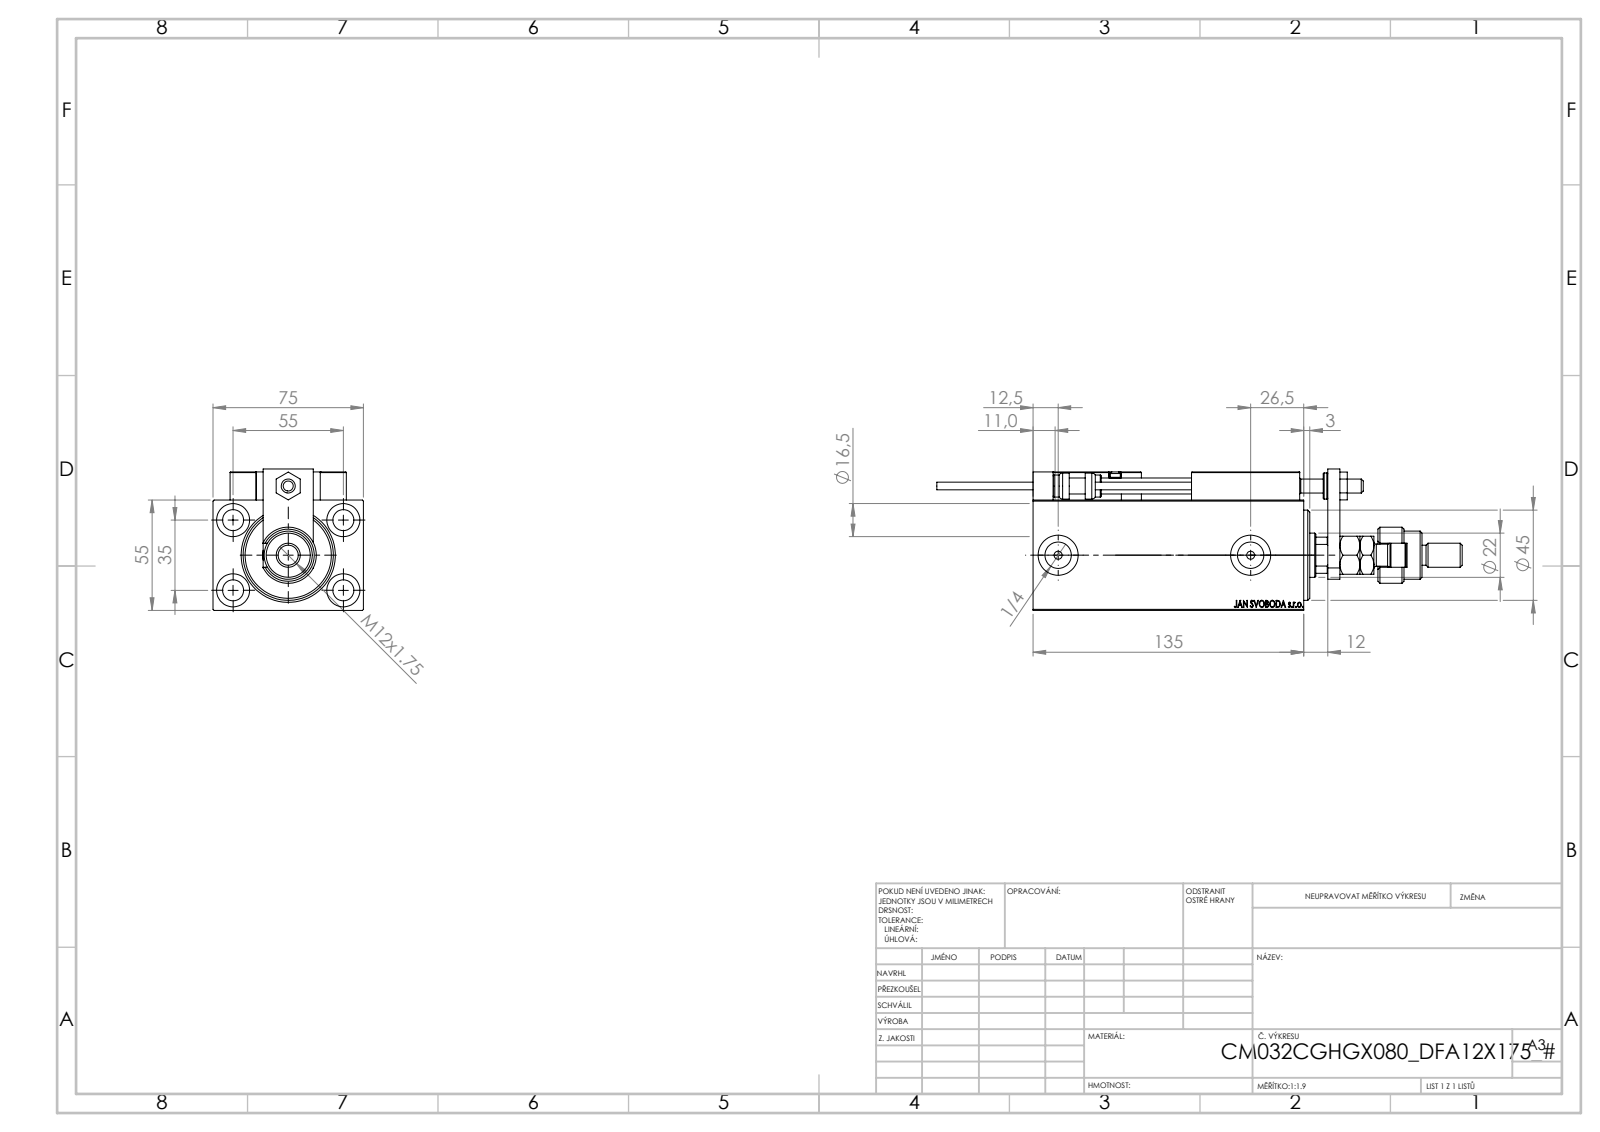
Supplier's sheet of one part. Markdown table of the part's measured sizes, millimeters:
| quantity | value |
| --- | --- |
| part name | V450CM_VC_B; TYC_L79; SWITCH_X_FRONT_BACK; SWITCH DIM B,W (+8 more) |
| STEP written by | SolidWorks 2019 (CONFIG_CONTROL_DESIGN) |
| units | millimeters |
| bodies | 25 solids, 1367 faces (588 planar, 201 cylindrical, 578 other) |
| overall size | 262 × 75 × 70.5 |
| volume | 535 346 mm³ |
| surface area | 128 651 mm² |
| round holes (diameter × count) | 4 × 6, 8 × 5, 10.5 × 5, 16.5 × 5, 3.2 × 4, 5 × 2, 13.16 × 2, 20 × 2, 7 × 1, 22 × 1, 25.5 × 1, 32 × 1 |
| round bosses / shafts (diameter × count) | 11 × 2, 5 × 2, 3.8 × 2, 28 × 1, 24 × 1, 18 × 1, 13 × 1, 12 × 1 |
| partial cylindrical surfaces (radius × count) | 0.3 × 30, 3 × 2, 9.75 × 1, 10.5 × 1 |
| main face-to-face distances | 55, 75, 14, 10, 25, 69, 18, 12, 6, 3 |
| hole center spacings | 32.6, 11.37, 20, 29.59, 29.69, 32.33, 35, 36.06 |
